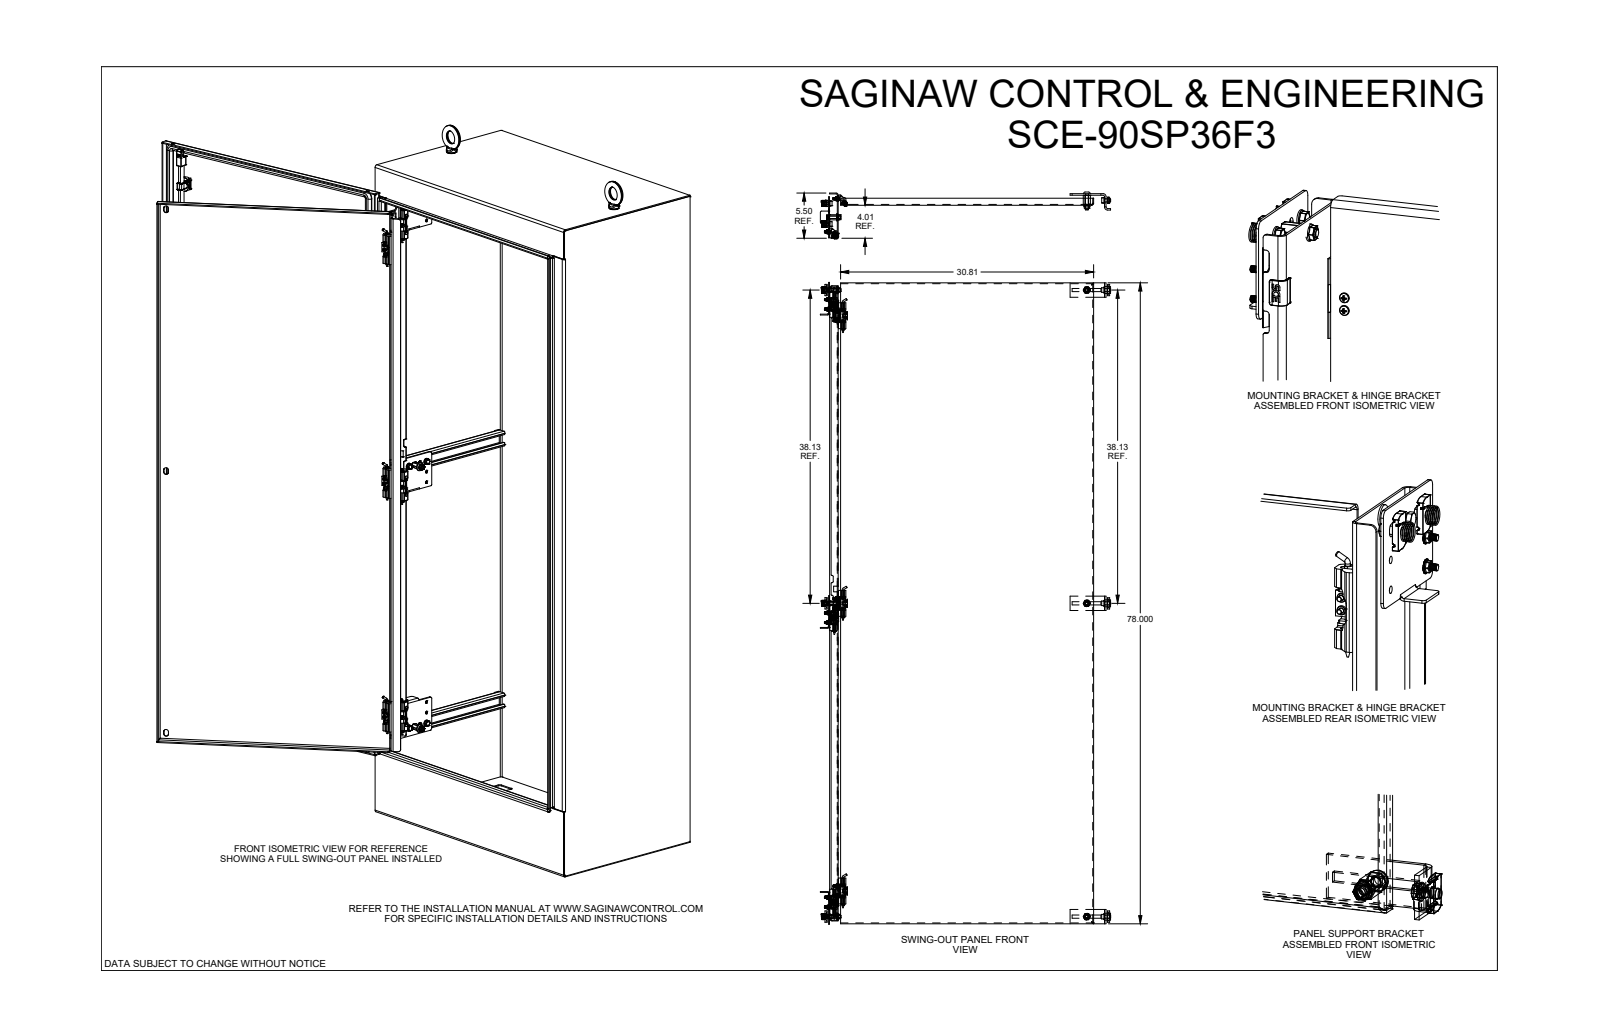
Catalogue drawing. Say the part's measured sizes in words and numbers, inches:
The part is named "SCE-90SP36F3". Its 3-D file was written by "SolidWorks 2021 (AUTOMOTIVE_DESIGN)". It is 50 solids with 2520 faces: 1192 planar, 988 cylindrical and 340 other. Overall it measures 78.119 by 35.336 by 5.681 inches. Its volume is 339.5 cubic inches and its surface area 6 501 square inches. Round holes: 18 of diameter 0.25, 18 of diameter 0.281, 12 of diameter 0.36, 9 of diameter 0.218, 6 of diameter 0.04, 6 of diameter 0.19, 3 of diameter 0.156, 3 of diameter 0.33, 3 of diameter 0.383, 2 of diameter 0.201, 2 of diameter 0.375, 1 of diameter 0.204. Round bosses or shafts: 8 of diameter 0.196, 6 of diameter 0.34, 6 of diameter 0.249, 3 of diameter 0.886, 3 of diameter 0.813, 3 of diameter 0.5, 3 of diameter 0.368, 3 of diameter 0.31. Partial cylindrical surfaces (rounded edges, fillets, slot ends): 54 of radius 0.011, 37 of radius 0.188, 28 of radius 0.015, 22 of radius 0.25, 18 of radius 0.1, 17 of radius 0.06, 16 of radius 0.03, 14 of radius 0.13. The main face-to-face distances are 0.104, 1.385, 1.058, 31.108, 32.166, 5.396, 4.011, 1.281, 1.489, 0.954. The hole center spacings are 0.592, 35, 38.125, 1.181, 34.625, 72.75, 2.098, 3.5.
